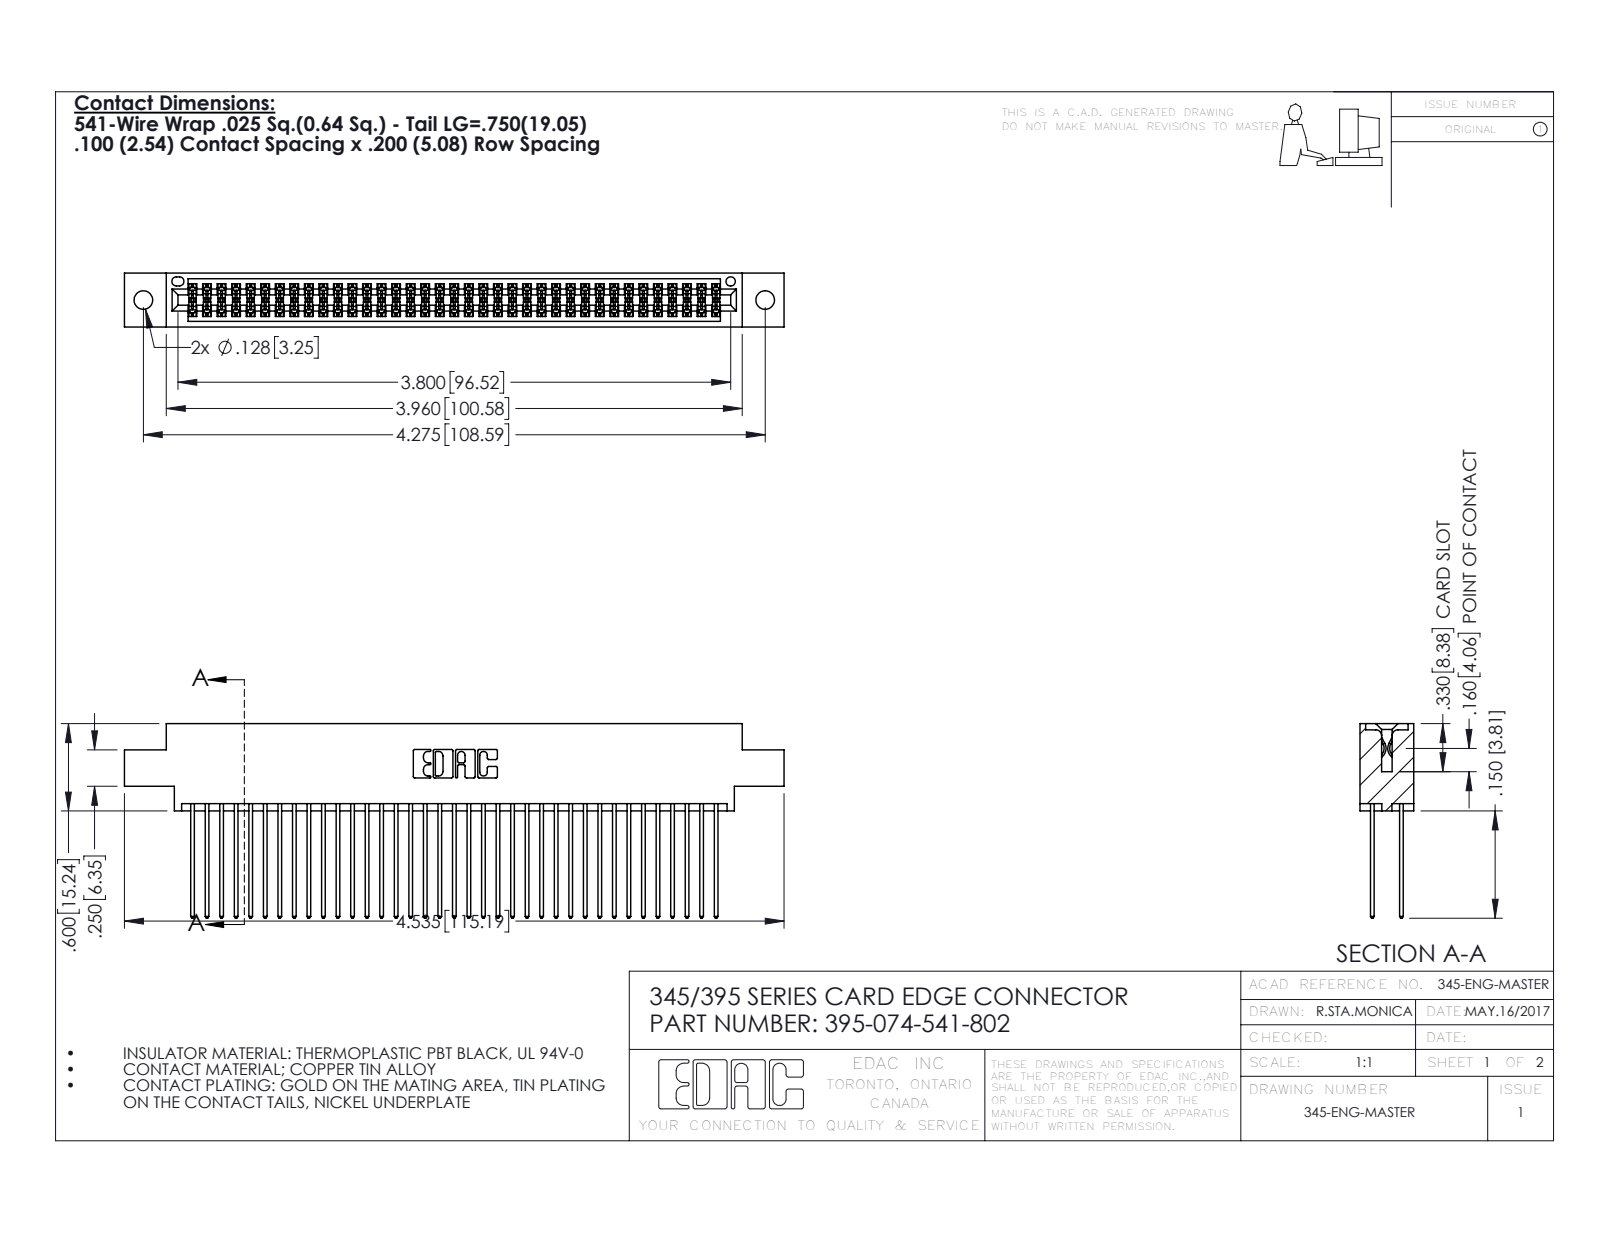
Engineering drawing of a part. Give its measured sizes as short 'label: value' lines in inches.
name: 345-292-001_345-293-141; 395-074-541-802; 345 Part_0.170 Offset - 0.128 Dia
written by: SolidWorks 2016 (CONFIG_CONTROL_DESIGN)
unit: in
bodies: 75 solids, 3830 faces (2526 planar, 1304 cylindrical, 0 other)
size: 4.535 × 1.337 × 0.37
volume: 0.697 in³; area: 28.9 in²
holes: 2× ⌀0.128, 1× ⌀0.064
rounds: 111× R0.006, 74× R0.01, 22× R0.01, 6× R0.007, 6× R0.031, 3× R0.026, 2× R0.014, 2× R0.019
face distances: 0.298, 0.072, 0.2, 0.098, 0.272, 0.025, 0.37, 0.225, 0.175, 0.149
hole spacings: 0.27, 4.039, 4.275
